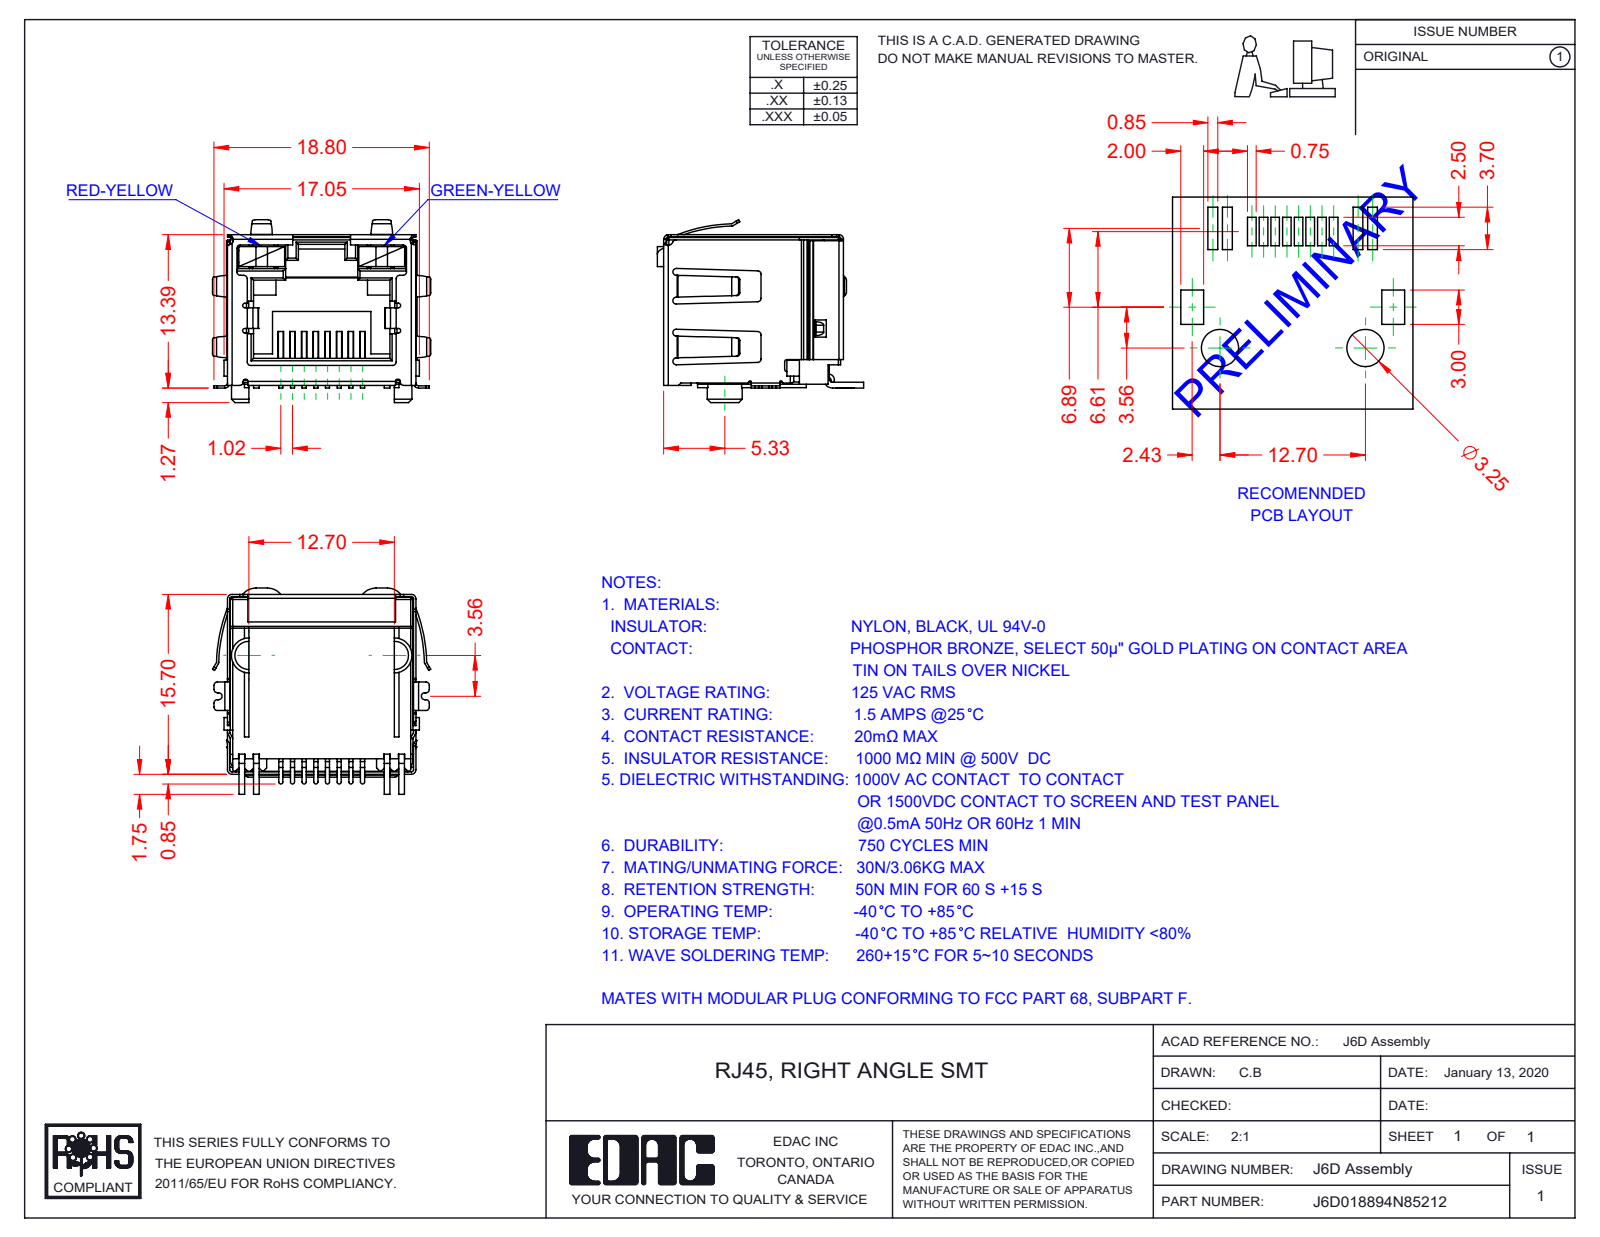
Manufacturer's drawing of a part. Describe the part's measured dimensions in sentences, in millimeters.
The part is named "J6D018894N85212; 6D Shield_LED - EMI; 6D Contacts; 6D LED RH_5-Green-Yellow (+2 more)". Its 3-D file was written by "SolidWorks 2016 (CONFIG_CONTROL_DESIGN)". It is 12 solids with 1034 faces: 703 planar, 286 cylindrical and 45 other. Overall it measures 19.06 by 18 by 15.95 millimeters. Its volume is 1 790 cubic millimeters and its surface area 4 796 square millimeters. Partial cylindrical surfaces (rounded edges, fillets, slot ends): 55 of radius 0.3, 40 of radius 0.2, 19 of radius 0.4, 16 of radius 0.25, 12 of radius 0.1, 8 of radius 0.15, 8 of radius 0.18, 6 of radius 0.5. The main face-to-face distances are 16, 16.2, 16.25, 2.25, 1, 15.95, 12.8, 0.45, 13.05, 10.6.
